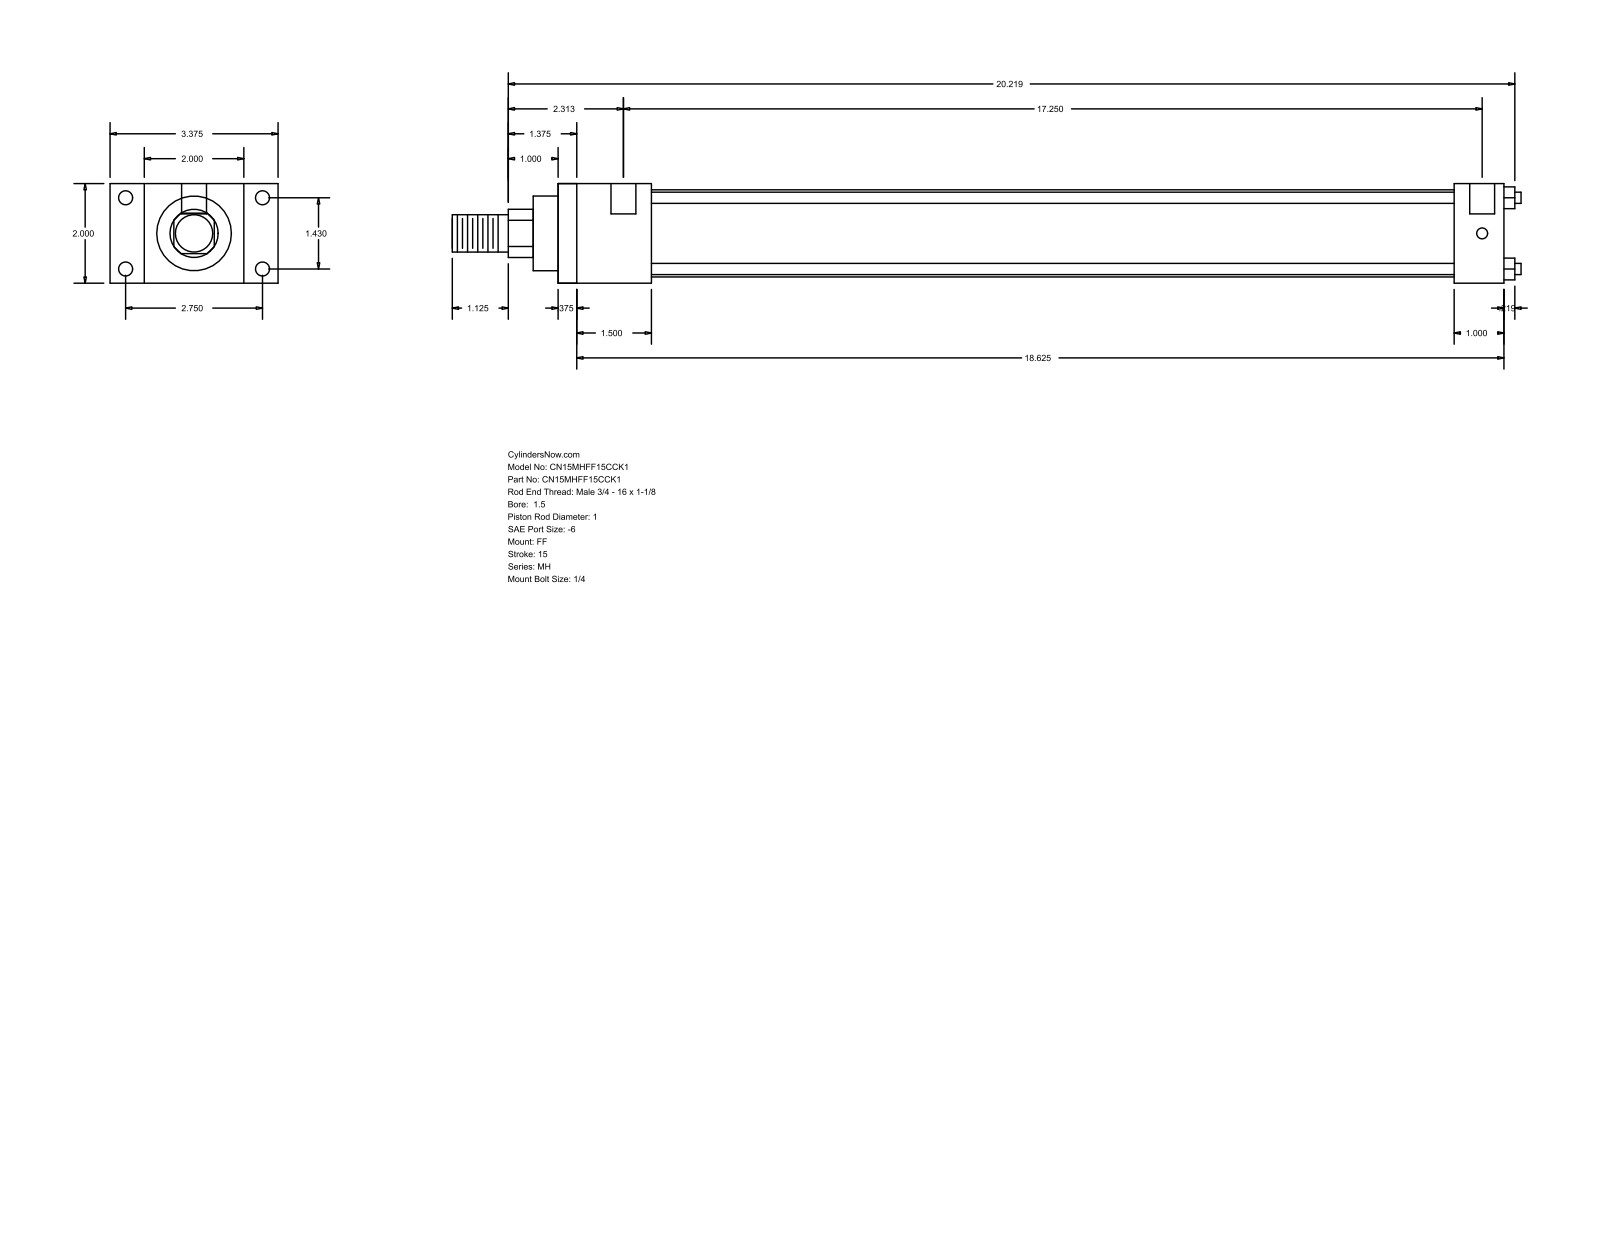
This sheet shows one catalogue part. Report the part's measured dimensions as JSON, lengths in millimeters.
{"part_name": "MH_FF__0150_1", "step_written_by": "GSSL Pune (CONFIG_CONTROL_DESIGN)", "units": "millimeters", "bodies": {"solids": 0, "faces": 92, "planar": 64, "cylindrical": 28, "other": 0}, "overall_size": [545.31, 85.72, 50.8], "round_holes": [[5.56, 4], [7.14, 4], [12.7, 2]], "round_bosses_or_shafts": [[5.71, 4], [44.45, 1], [38.1, 1], [25.4, 1], [19.05, 1]], "partial_cylinders_radius": [[12.29, 1]], "face_to_face_distances": [50.8, 482.6, 9.52, 473.08, 25.4, 17.46, 68.26, 47.63, 38.11, 434.97], "hole_center_spacings": [36.32, 69.84, 78.72, 441.33, 3.18, 438.15]}
